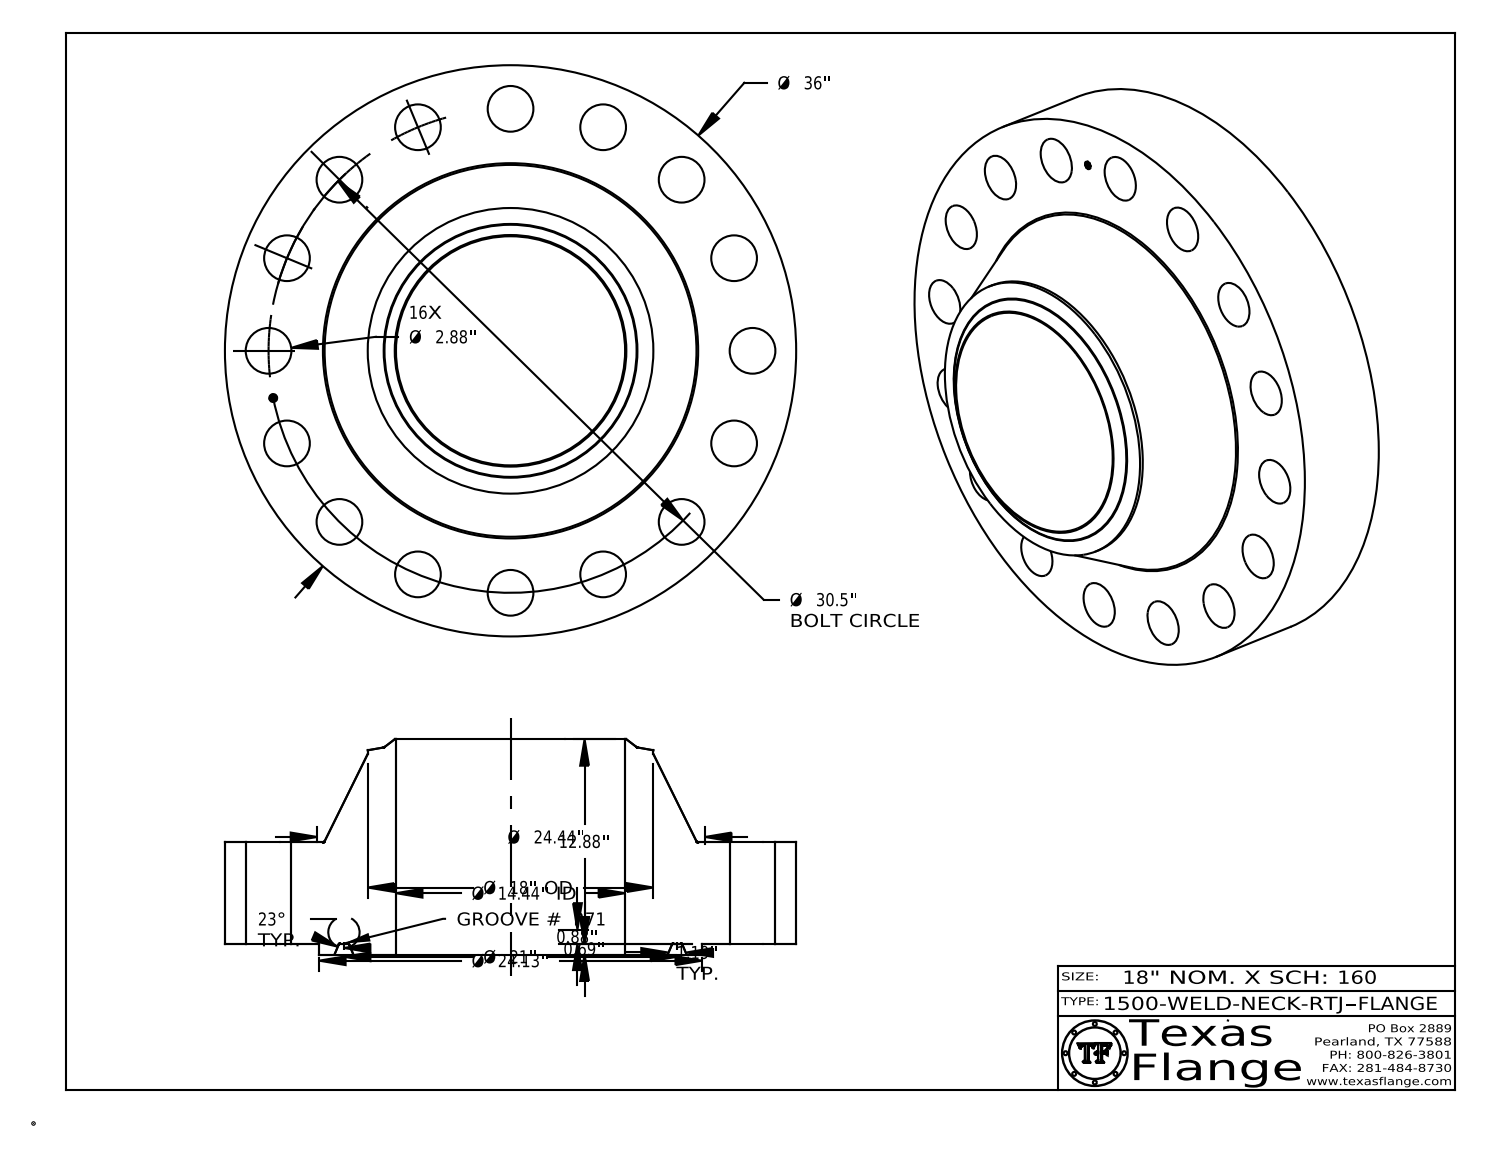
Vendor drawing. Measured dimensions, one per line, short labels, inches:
name: 1500-WELD-NECK-RTJ
written by: CATIA V5 STEP AP214 (AUTOMOTIVE_DESIGN)
unit: in
bodies: 1 solid, 449 faces (371 planar, 60 cylindrical, 18 other)
size: 36 × 36 × 13.568
volume: 5 971 in³; area: 4 118 in²
holes: 16× ⌀2.88, 1× ⌀0.495, 1× ⌀14.438
bosses: 8× ⌀0.03, 1× ⌀36, 1× ⌀24.125, 1× ⌀18, 1× ⌀0.39
face distances: 6.38, 0.688, 7.068, 13.568, 12.88, 6.5, 7.053, 6.365, 0.015, 6.515
hole spacings: 5.95, 16.945, 29.914, 15.25, 11.672, 11.672, 15.25, 21.567
